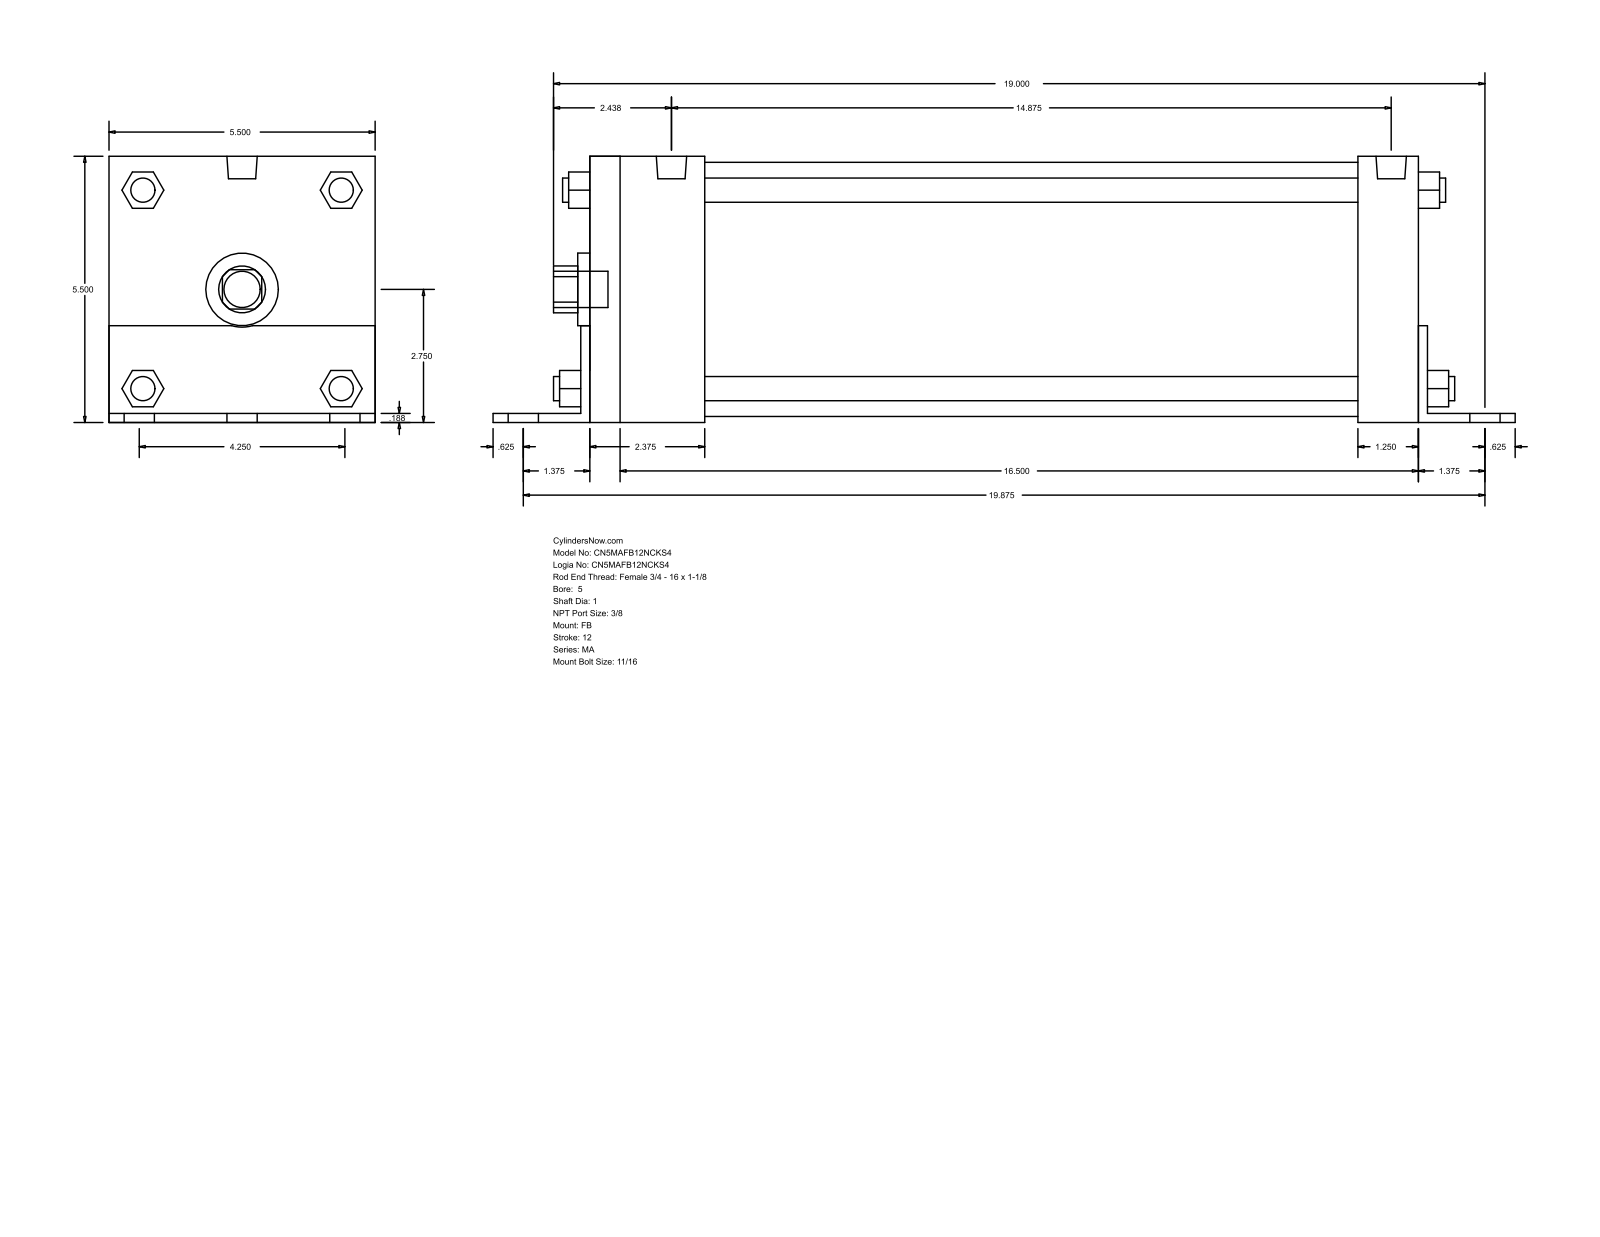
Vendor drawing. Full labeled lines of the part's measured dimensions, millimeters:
Part name (STEP PRODUCT): MA_FB__0500_1
STEP written by: GSSL Pune (CONFIG_CONTROL_DESIGN)
Units: millimetres
Bodies: 0 solids, 140 faces (105 planar, 35 cylindrical, 0 other)
Overall size (bounding box): 536.58 × 139.75 × 139.7
Round holes (diameter × count): ⌀25.4 ×1, ⌀38.1 ×1, ⌀133.35 ×1
Round bosses / shafts (diameter × count): ⌀17.46 ×6, ⌀12.7 ×4, ⌀11.11 ×4, ⌀15.93 ×2, ⌀19.05 ×1
Partial cylindrical surfaces — rounded edges, fillets, slot ends (radius × count): R12.29 ×1, R19.81 ×1
Main face-to-face distances: 139.7, 4.76, 139.75, 4.71, 134.99, 434.97, 4.77, 439.74, 444.5, 439.73
